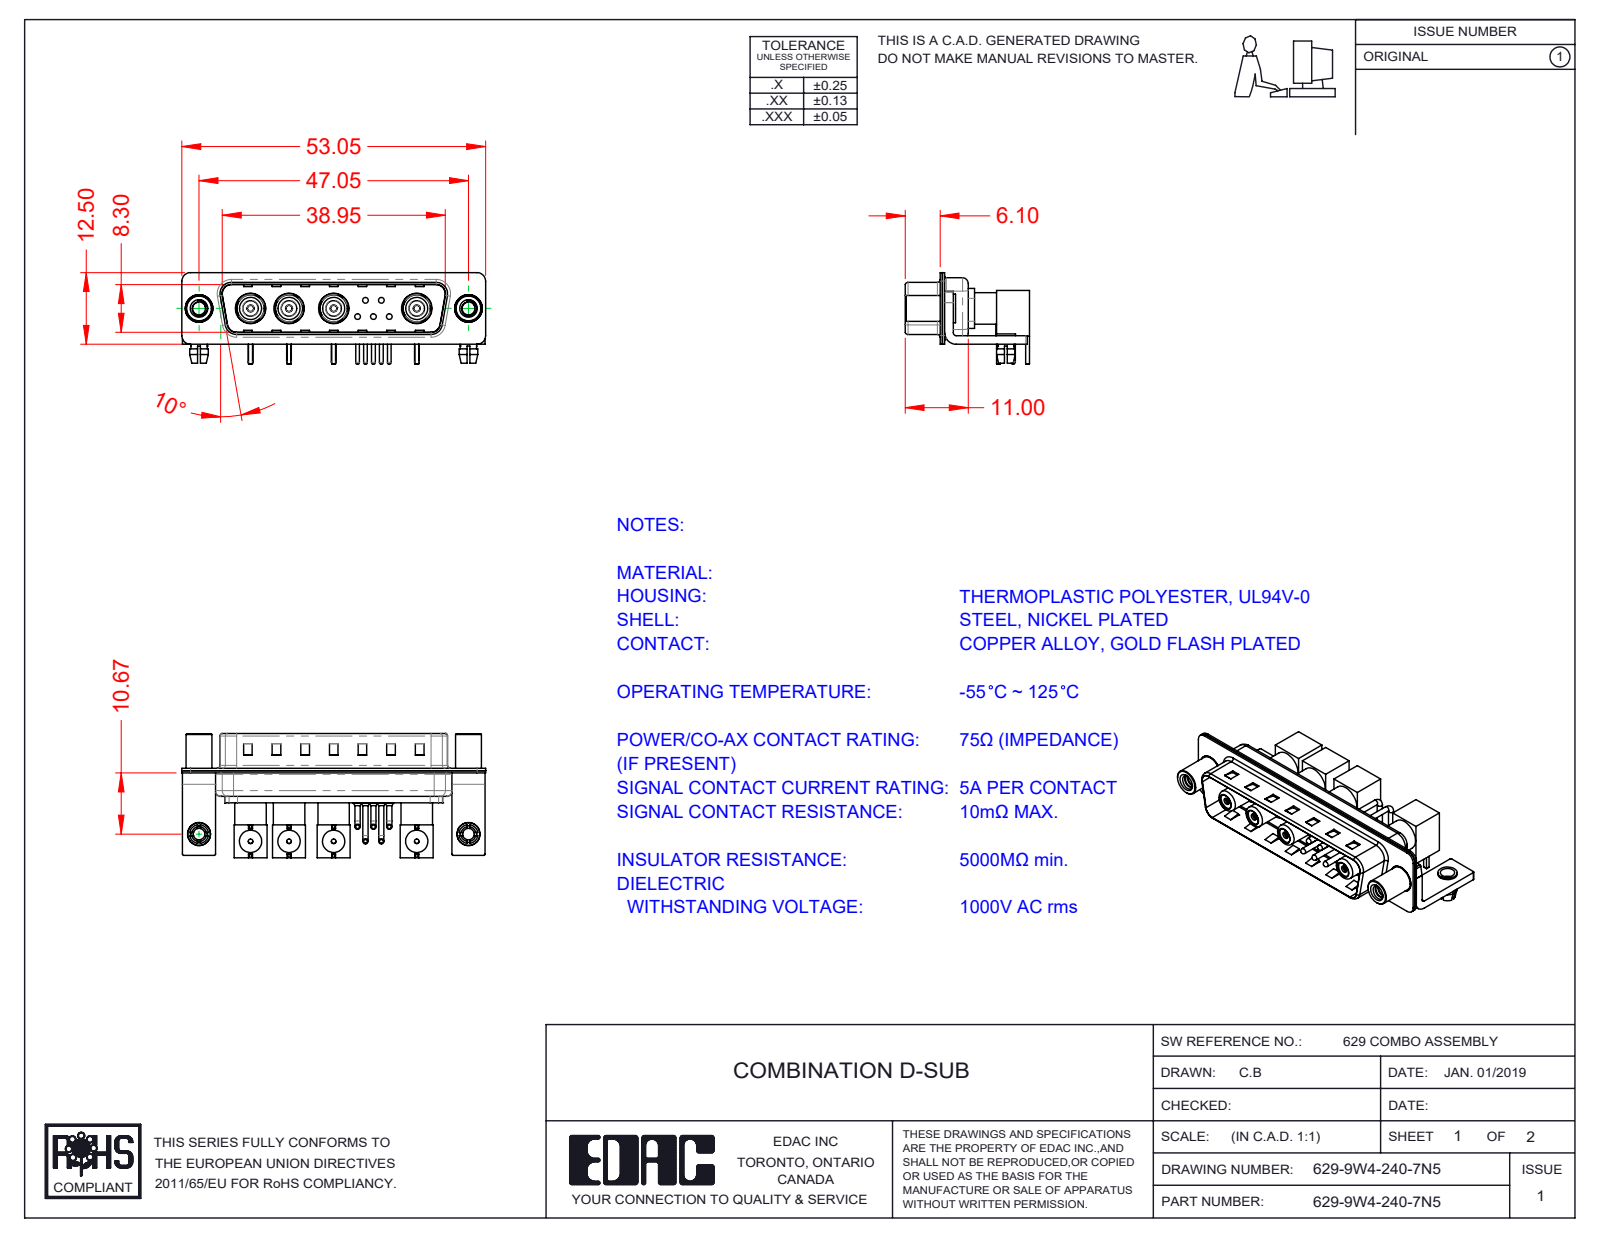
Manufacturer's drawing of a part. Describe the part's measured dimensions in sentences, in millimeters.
The part is named "Insulator Socket; 629-9W4-240-7N5; Co-Ax Jack Assy_RA; Socket_RA (+8 more)". Its 3-D file was written by "SolidWorks 2020 (CONFIG_CONTROL_DESIGN)". It is 42 solids with 1714 faces: 789 planar, 677 cylindrical and 248 other. Overall it measures 53.05 by 21.71 by 16 millimeters. Its volume is 4 330 cubic millimeters and its surface area 11 754 square millimeters. Round holes: 9 of diameter 1.6, 7 of diameter 2, 6 of diameter 2.5, 5 of diameter 0.75, 4 of diameter 0.8, 4 of diameter 1.1, 4 of diameter 1.2, 4 of diameter 1.5, 4 of diameter 2.7, 4 of diameter 3.1, 4 of diameter 3.4, 4 of diameter 3.9. Round bosses or shafts: 10 of diameter 0.9, 8 of diameter 0.8, 6 of diameter 4, 6 of diameter 3.3, 6 of diameter 2.9, 5 of diameter 1.5, 5 of diameter 1, 5 of diameter 0.65. Partial cylindrical surfaces (rounded edges, fillets, slot ends): 16 of radius 0.25, 16 of radius 1.5, 13 of radius 2, 9 of radius 0.5, 8 of radius 1.6, 5 of radius 1.01, 4 of radius 0.6, 4 of radius 0.65. The main face-to-face distances are 0.4, 0.8, 9.5, 1.5, 5.75, 9.1, 8.7, 1.4, 9.9, 0.35. The hole center spacings are 14.51, 14.52, 6.72, 7.79, 22.3, 29.02, 3.16, 14.5.
